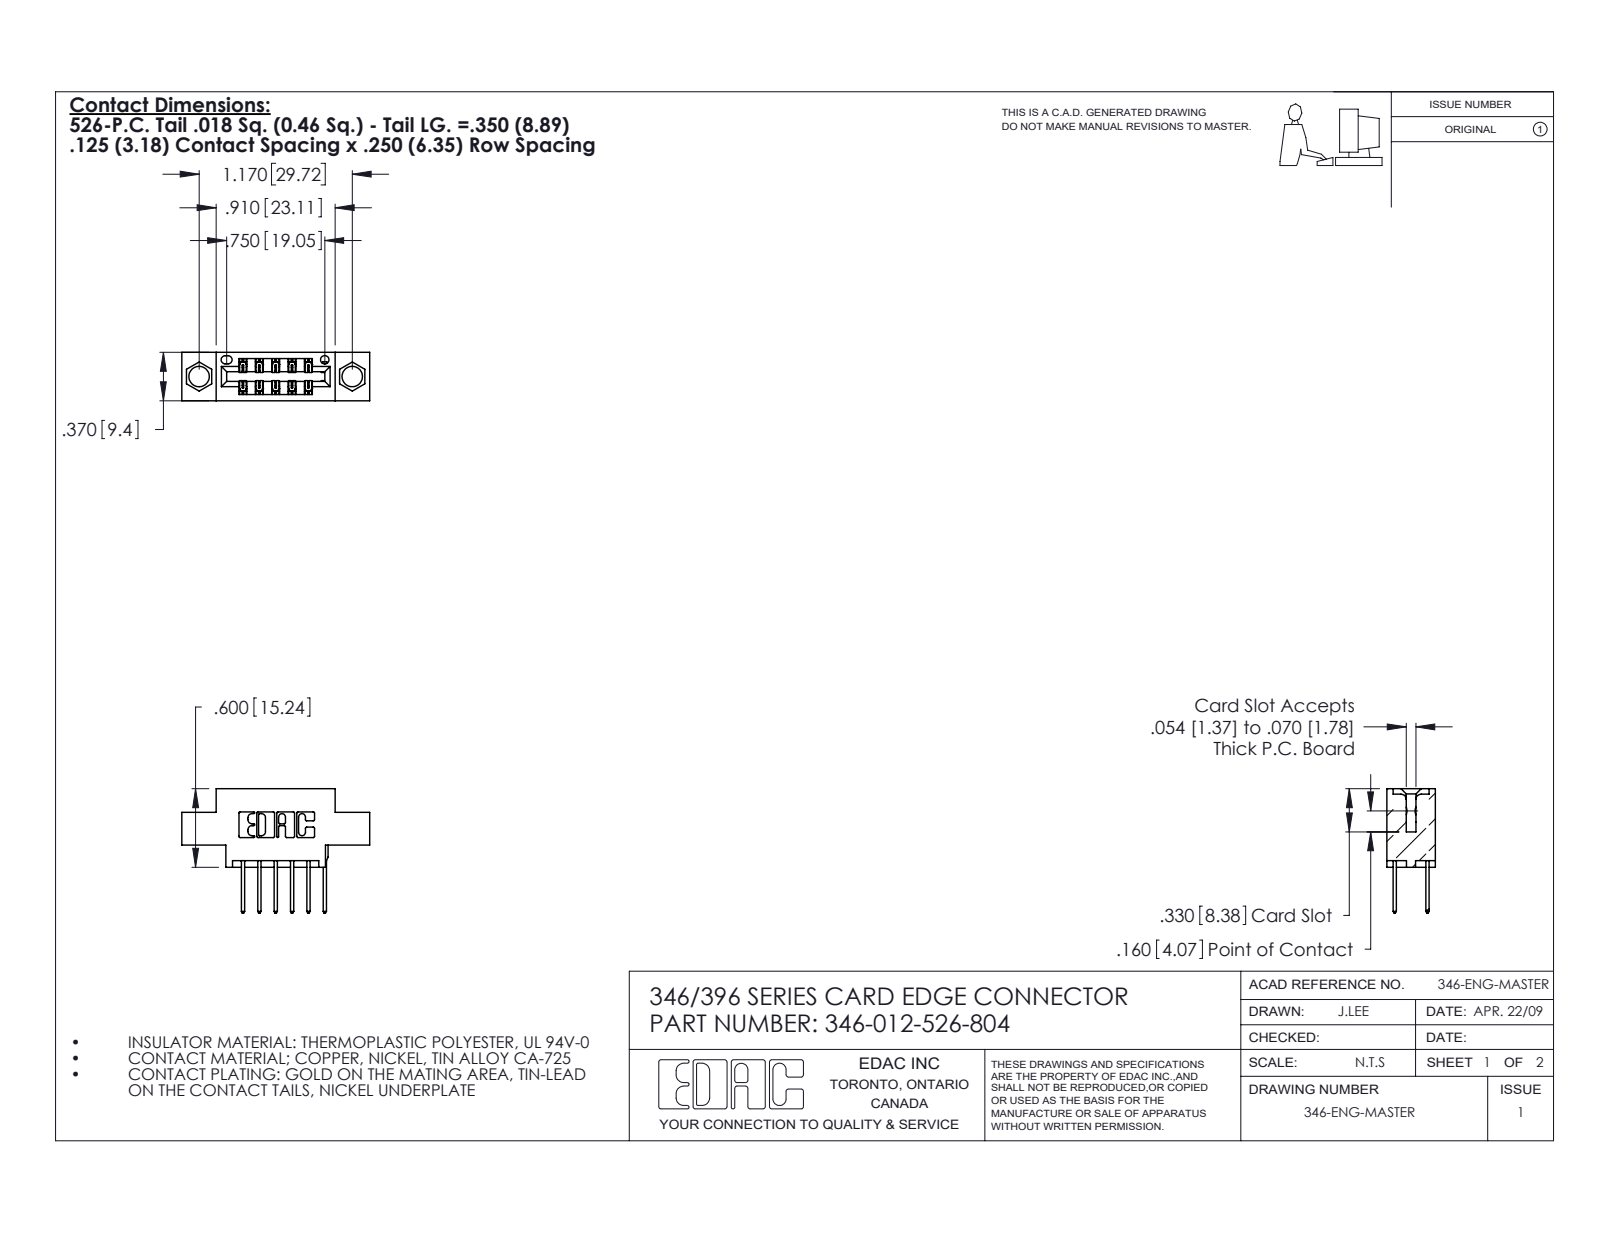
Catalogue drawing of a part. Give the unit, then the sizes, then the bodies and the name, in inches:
Units: inches
Overall size (bounding box): 1.435 × 0.95 × 0.37
Round holes (diameter × count): ⌀0.156 ×2, ⌀0.064 ×1
Partial cylindrical surfaces — rounded edges, fillets, slot ends (radius × count): R0.01 ×22, R0.006 ×18, R0.01 ×12, R0.007 ×6, R0.031 ×6, R0.026 ×3, R0.014 ×2, R0.022 ×2
Main face-to-face distances: 0.25, 0.37, 0.048, 0.322, 0.025, 0.072, 0.298, 0.275, 0.222, 0.225
Hole centre spacings: 0.246, 0.969, 1.17
Volume: 0.186 in³ · Surface area: 5.924 in²
Bodies: 13 solids, 752 faces (504 planar, 248 cylindrical, 0 other)
Part name (STEP PRODUCT): 346-012-526-804; 345-292-001_345-293-126; 346 Part_0.170 Offset - 0.156 Dia-TH
STEP written by: SolidWorks 2020 (CONFIG_CONTROL_DESIGN)
